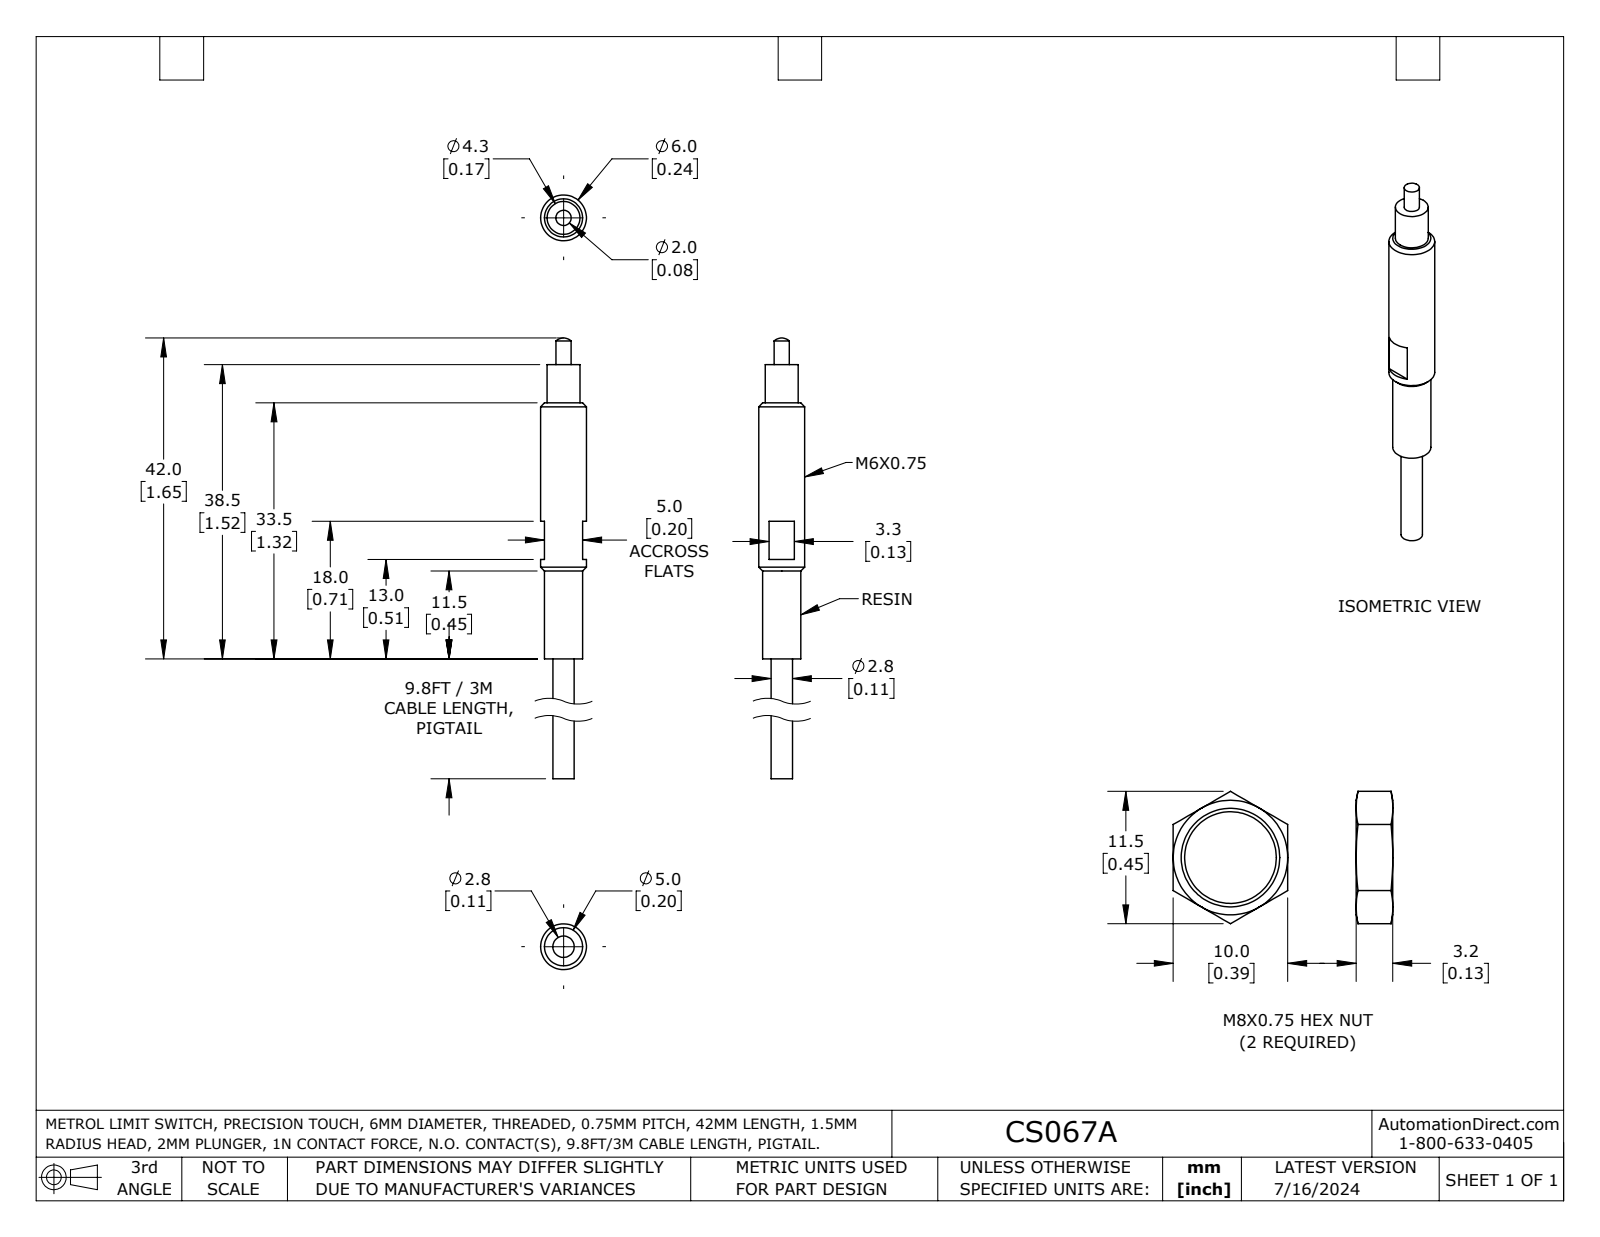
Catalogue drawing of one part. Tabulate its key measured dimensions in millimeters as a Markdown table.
| quantity | value |
| --- | --- |
| part name | CS067A |
| STEP written by | SolidWorks 2023 (AUTOMOTIVE_DESIGN) |
| units | millimeters |
| bodies | 1 solid, 18 faces (10 planar, 5 cylindrical, 3 other) |
| overall size | 56 × 6 × 6 |
| volume | 1 000 mm³ |
| surface area | 854 mm² |
| round bosses / shafts (diameter × count) | 6 × 1, 5 × 1, 4.3 × 1, 2.8 × 1, 2 × 1 |
| main face-to-face distances | 5, 38.5, 14, 52.5, 47.5, 33.5, 20.5, 27, 13, 25.5 |
